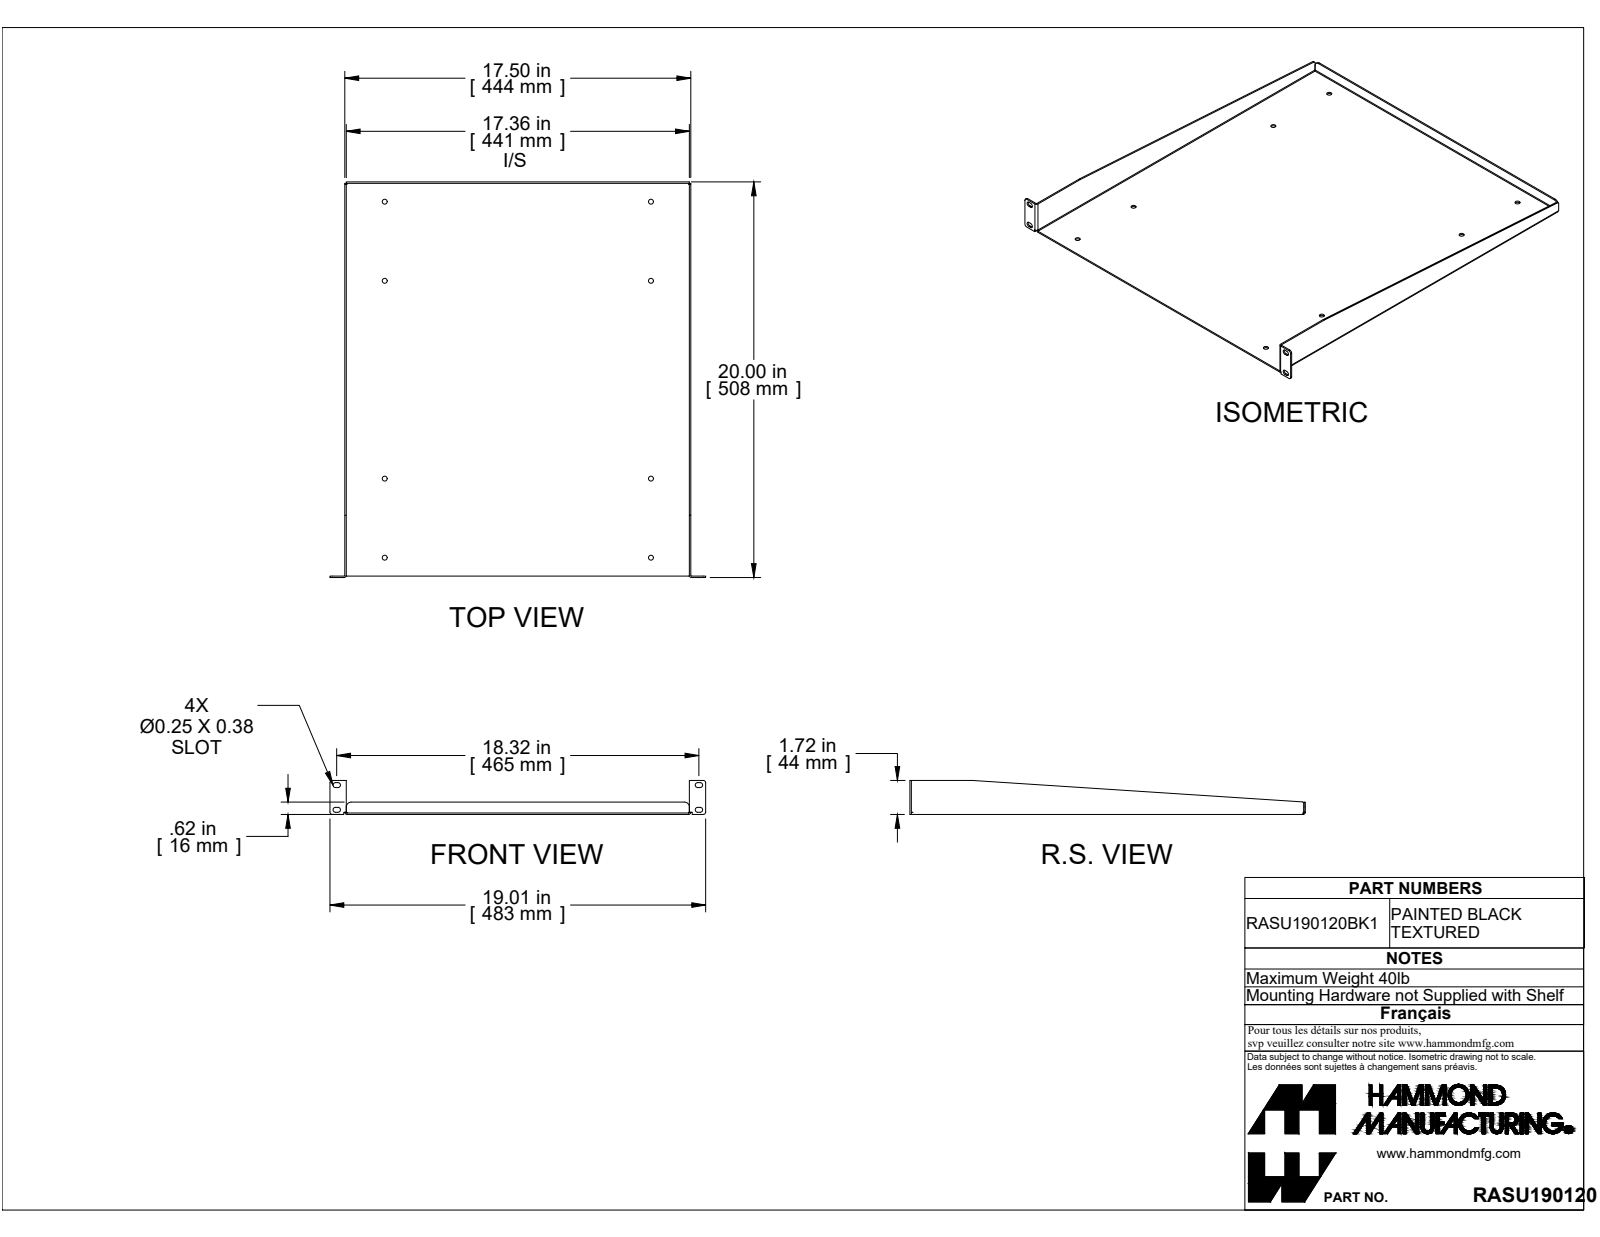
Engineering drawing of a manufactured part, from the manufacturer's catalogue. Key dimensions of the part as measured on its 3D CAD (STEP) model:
Part name (STEP PRODUCT): RASU190120BK1
STEP written by: SolidWorks 2019 (CONFIG_CONTROL_DESIGN)
Units: inches
Bodies: 1 solid, 88 faces (48 planar, 36 cylindrical, 4 other)
Overall size (bounding box): 20 × 19.006 × 1.718
Volume: 29.2 in³ · Surface area: 818 in²
Round holes (diameter × count): ⌀0.25 ×8
Partial cylindrical surfaces — rounded edges, fillets, slot ends (radius × count): R0.125 ×12, R0.036 ×5, R0.108 ×5, R0.055 ×3, R0.25 ×2
Main face-to-face distances: 0.072, 17.428, 17.356, 17.5, 19.856, 19.928, 0.072, 19.928, 20, 0.625
Hole centre spacings: 4, 13.468, 14, 14.049, 19.426, 10, 16.774, 18
